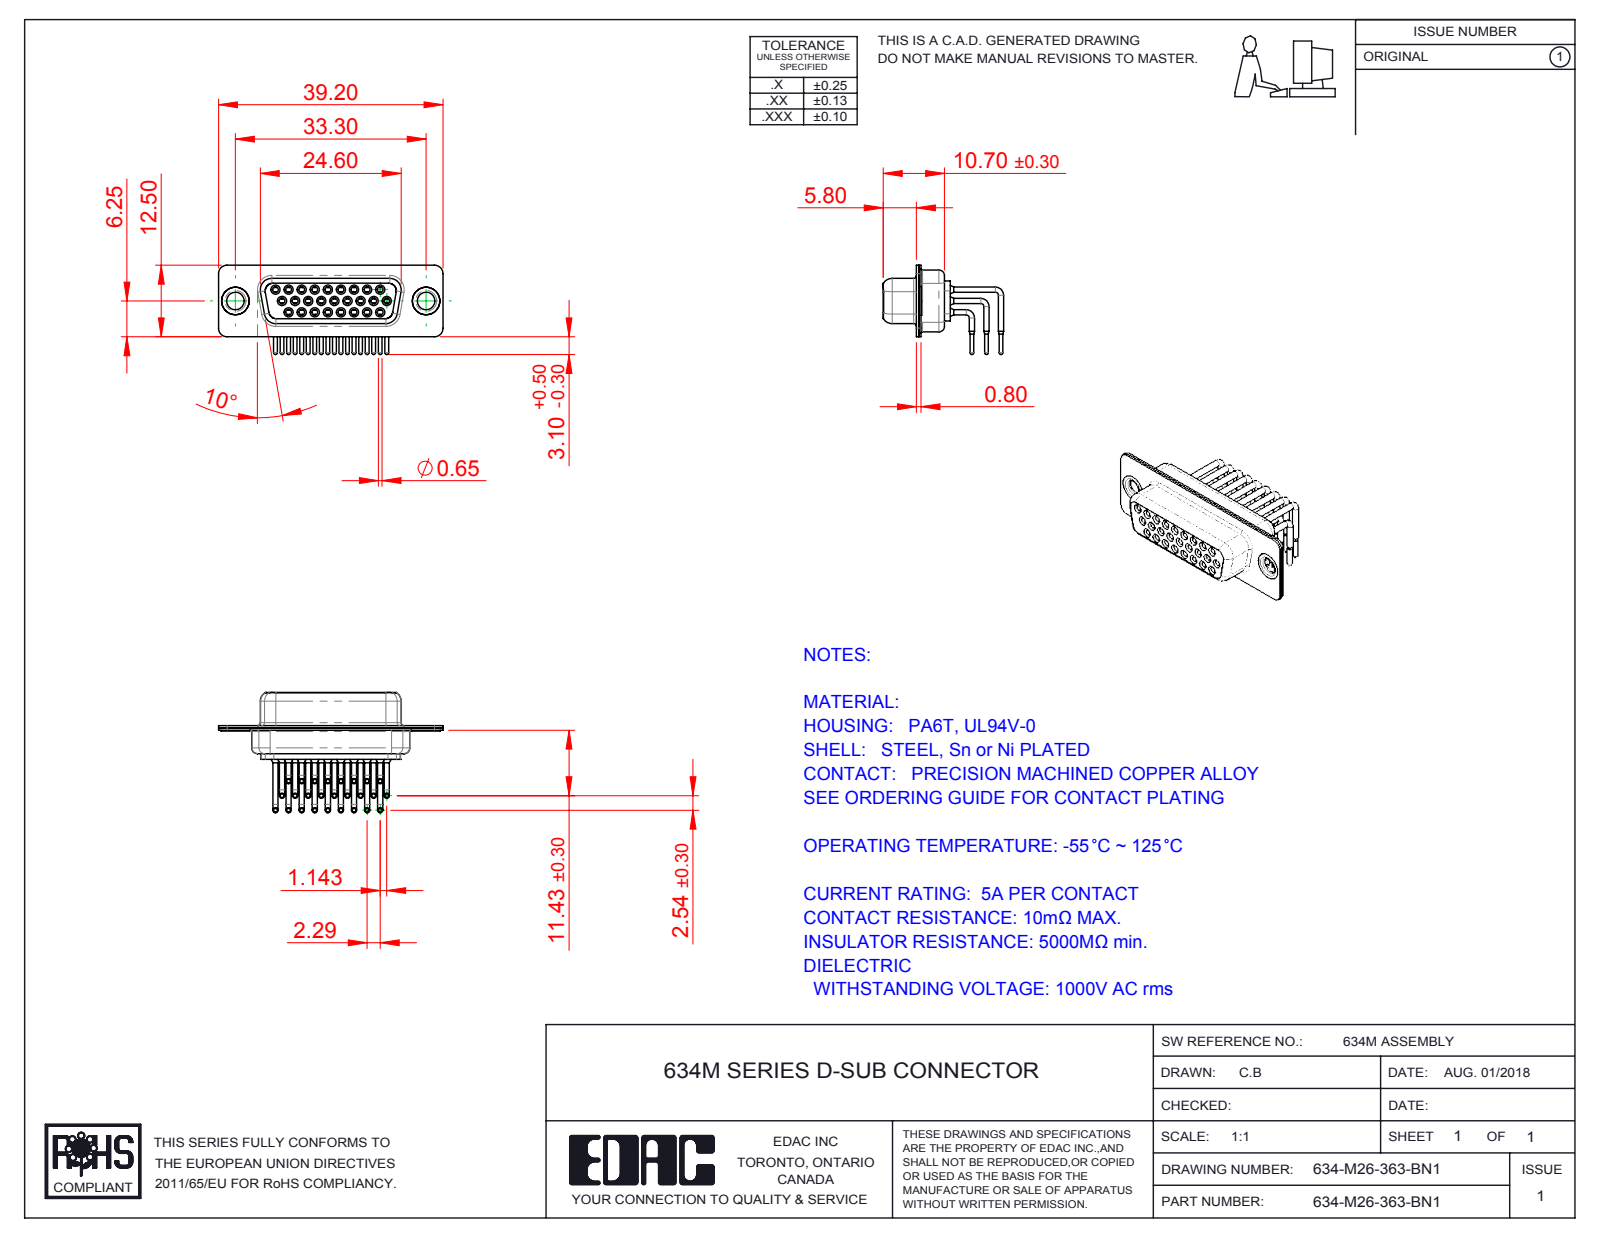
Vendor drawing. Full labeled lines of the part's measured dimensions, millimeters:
Part name (STEP PRODUCT): 634M Shell Rear_26 Contacts; 634M Shell Front_26 Contacts; 634M Contact Row 1; 634-M26-363-BN1 (+4 more)
STEP written by: SolidWorks 2016 (CONFIG_CONTROL_DESIGN)
Units: millimetres
Bodies: 31 solids, 1631 faces (457 planar, 719 cylindrical, 455 other)
Overall size (bounding box): 39.2 × 21.02 × 15.6
Volume: 2 454 mm³ · Surface area: 8 321 mm²
Round holes (diameter × count): ⌀1 ×26, ⌀1.1 ×26, ⌀1.7 ×26, ⌀1.8 ×26, ⌀2 ×26, ⌀3.05 ×2, ⌀4 ×2, ⌀4.8 ×2
Round bosses / shafts (diameter × count): ⌀0.9 ×52, ⌀1.6 ×26, ⌀1.5 ×26, ⌀0.65 ×26, ⌀5 ×2, ⌀4.9 ×2, ⌀3.55 ×2, ⌀2 ×1
Partial cylindrical surfaces — rounded edges, fillets, slot ends (radius × count): R1.5 ×16, R2 ×12, R1.35 ×8, R1.6 ×8, R0.25 ×4, R0.5 ×4, R0.6 ×4, R0.65 ×4
Main face-to-face distances: 0.4, 1.45, 8.95, 8.5, 1.9, 2.3, 0.8, 6.2, 0.45, 7.05
Hole centre spacings: 3.96, 2.28, 4.57, 6.05, 2.29, 8.24, 6.86, 6.04
